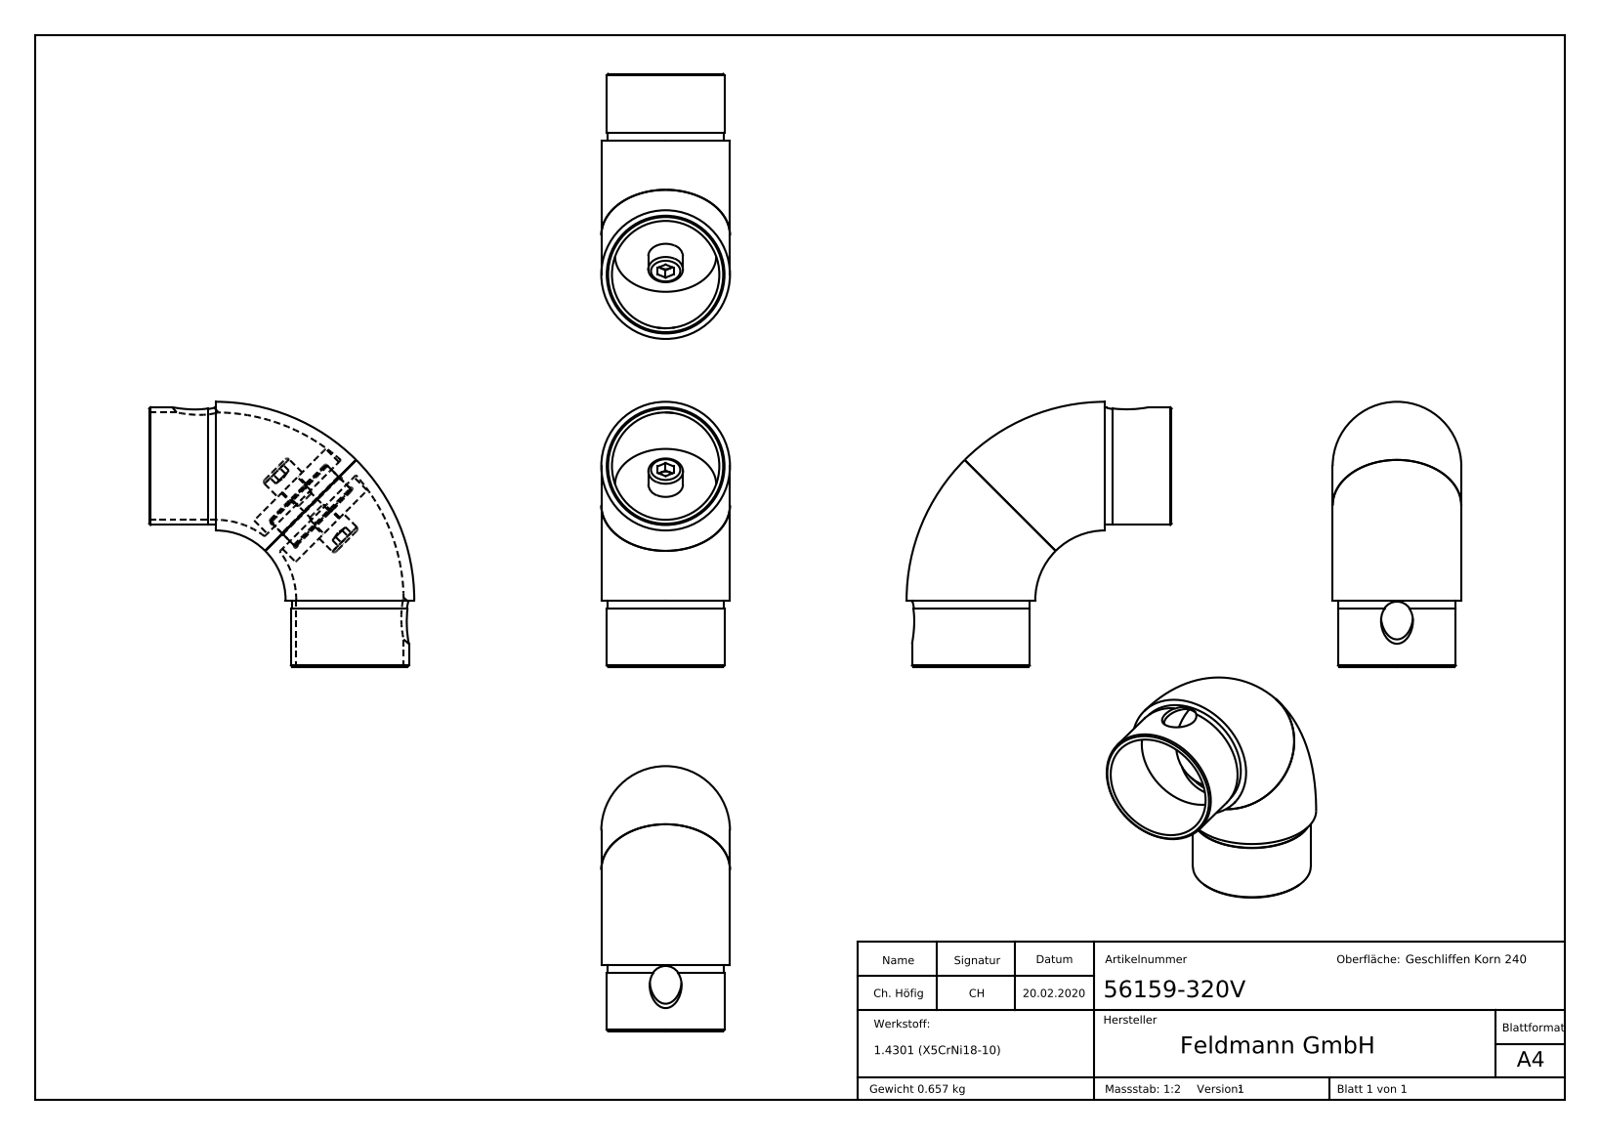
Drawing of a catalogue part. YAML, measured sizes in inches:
part_name: "56159-320V; 5616X-320V Teil1_56159-320V Teil1; 5616X-320V Teil2_56159-320V Teil2; DIN 912 Konfig (+3 more)"
step_written_by: "SolidWorks 2015 (CONFIG_CONTROL_DESIGN)"
units: inches
bodies: {solids: 5, faces: 552, planar: 290, cylindrical: 20, other: 242}
overall_size: [549.417, 488.952, 394.076]
volume: 5.078
surface_area: 75.31
round_holes:
  - {diameter: 0.354, count: 2}
  - {diameter: 0.472, count: 2}
  - {diameter: 1.181, count: 2}
  - {diameter: 1.587, count: 2}
  - {diameter: 0.268, count: 1}
round_bosses_or_shafts:
  - {diameter: 1.74, count: 2}
  - {diameter: 1.724, count: 2}
  - {diameter: 1.496, count: 2}
  - {diameter: 0.512, count: 2}
  - {diameter: 0.315, count: 2}
face_to_face_distances: [0.433, 0.157, 0.276, 0.866, 0.177, 0.689, 0.256, 0.709, 0.02, 0.531]
